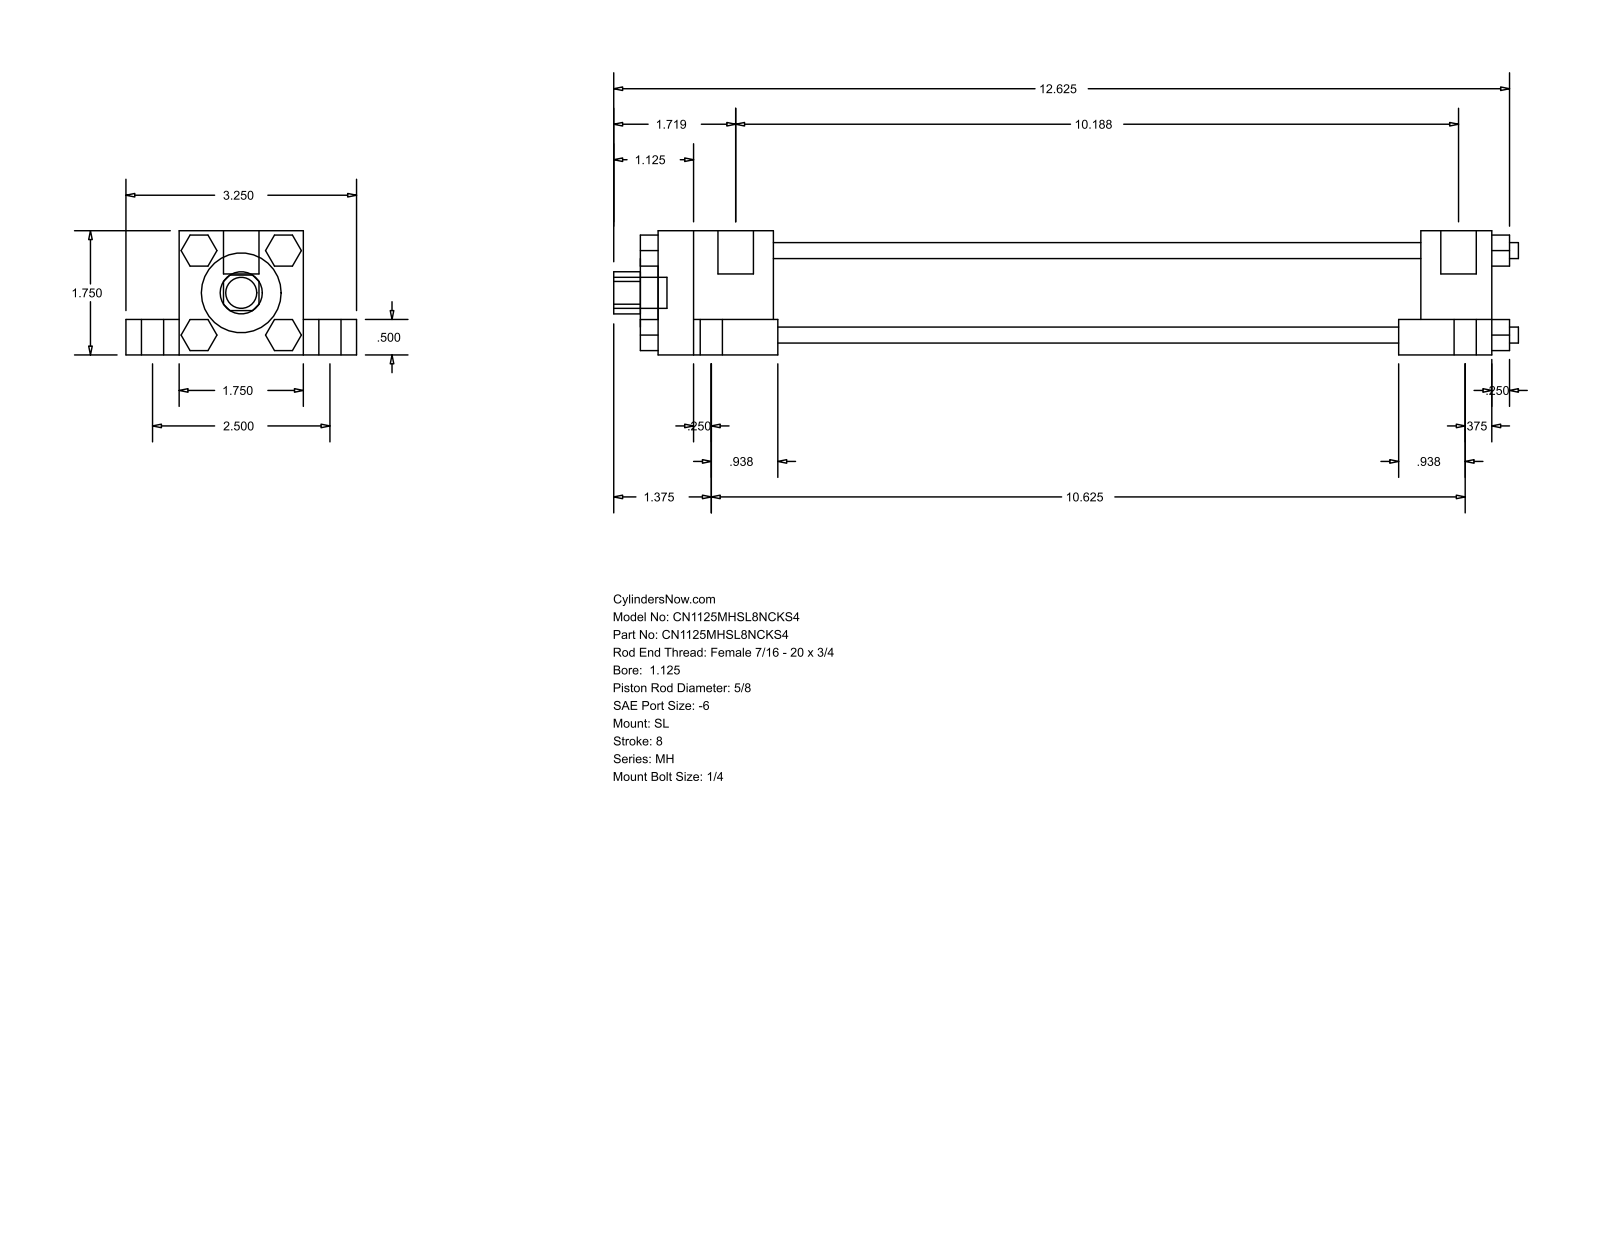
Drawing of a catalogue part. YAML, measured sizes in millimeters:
part_name: "MH_SL__0112_0.625"
step_written_by: "GSSL Pune (CONFIG_CONTROL_DESIGN)"
units: millimeters
bodies: {solids: 0, faces: 150, planar: 114, cylindrical: 36, other: 0}
overall_size: [323.85, 82.55, 44.45]
round_holes:
  - {diameter: 15.88, count: 1}
  - {diameter: 28.57, count: 1}
  - {diameter: 34.92, count: 1}
round_bosses_or_shafts:
  - {diameter: 14.29, count: 4}
  - {diameter: 7.94, count: 4}
  - {diameter: 5.71, count: 4}
  - {diameter: 5.56, count: 4}
  - {diameter: 12.7, count: 2}
  - {diameter: 11.11, count: 1}
partial_cylinders:
  - {radius: 7.54, count: 1}
face_to_face_distances: [44.46, 19.04, 12.7, 31.76, 63.5, 11.11, 231.78, 257.17, 25.39, 41.27]
